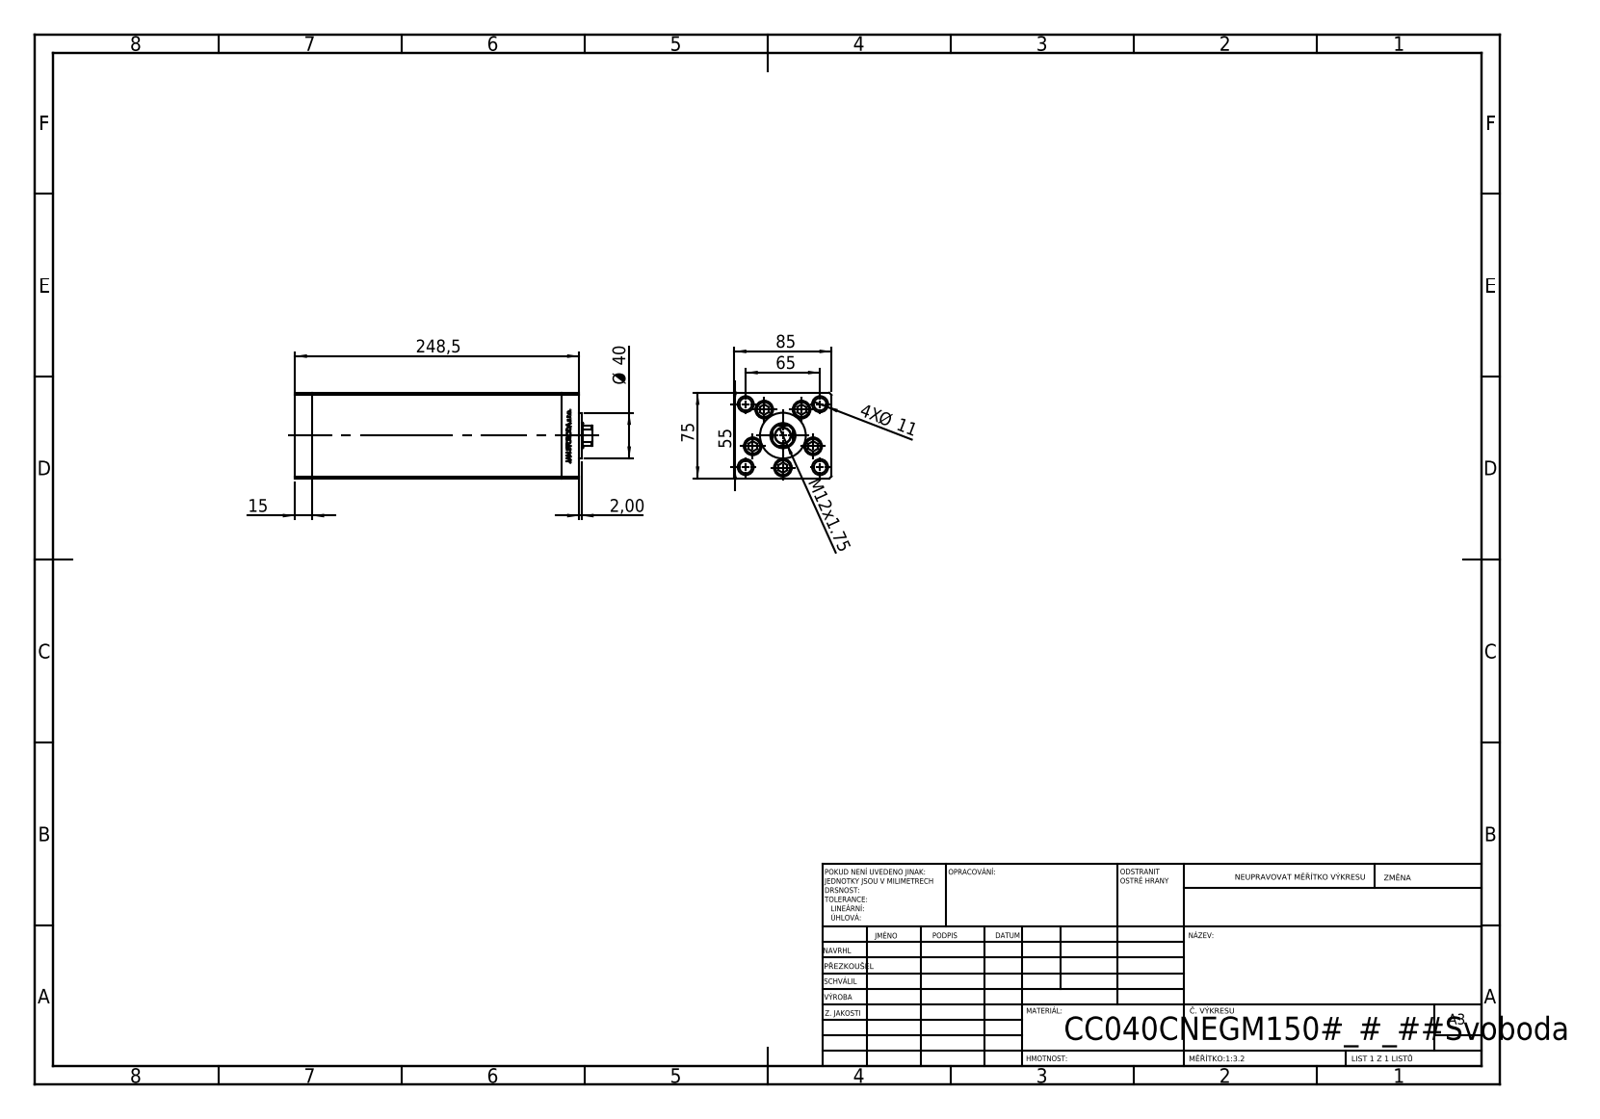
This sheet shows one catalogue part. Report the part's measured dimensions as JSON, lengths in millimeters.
{"part_name": "V220C_VC_C; V220C BACK_C; V220C_C MIDDLE; V220C FRONT (+1 more)", "step_written_by": "SolidWorks 2019 (CONFIG_CONTROL_DESIGN)", "units": "millimeters", "bodies": {"solids": 13, "faces": 1163, "planar": 542, "cylindrical": 159, "other": 462}, "overall_size": [260, 85, 75], "volume_mm3": 1314000, "surface_area_mm2": 219564, "round_holes": [[11, 9], [15.5, 5], [10, 4], [14, 4], [13.5, 1], [14.5, 1], [22, 1]], "round_bosses_or_shafts": [[8, 5], [14.5, 4], [40, 1]], "partial_cylinders_radius": [[0.93, 2], [10.5, 1]], "face_to_face_distances": [85, 75, 15, 218.5, 233.5, 10.5, 248.5, 34.25, 68.5, 64.5], "hole_center_spacings": [28, 42.57, 16.86, 19.17, 32.33, 32.5, 33.63, 37.33]}
